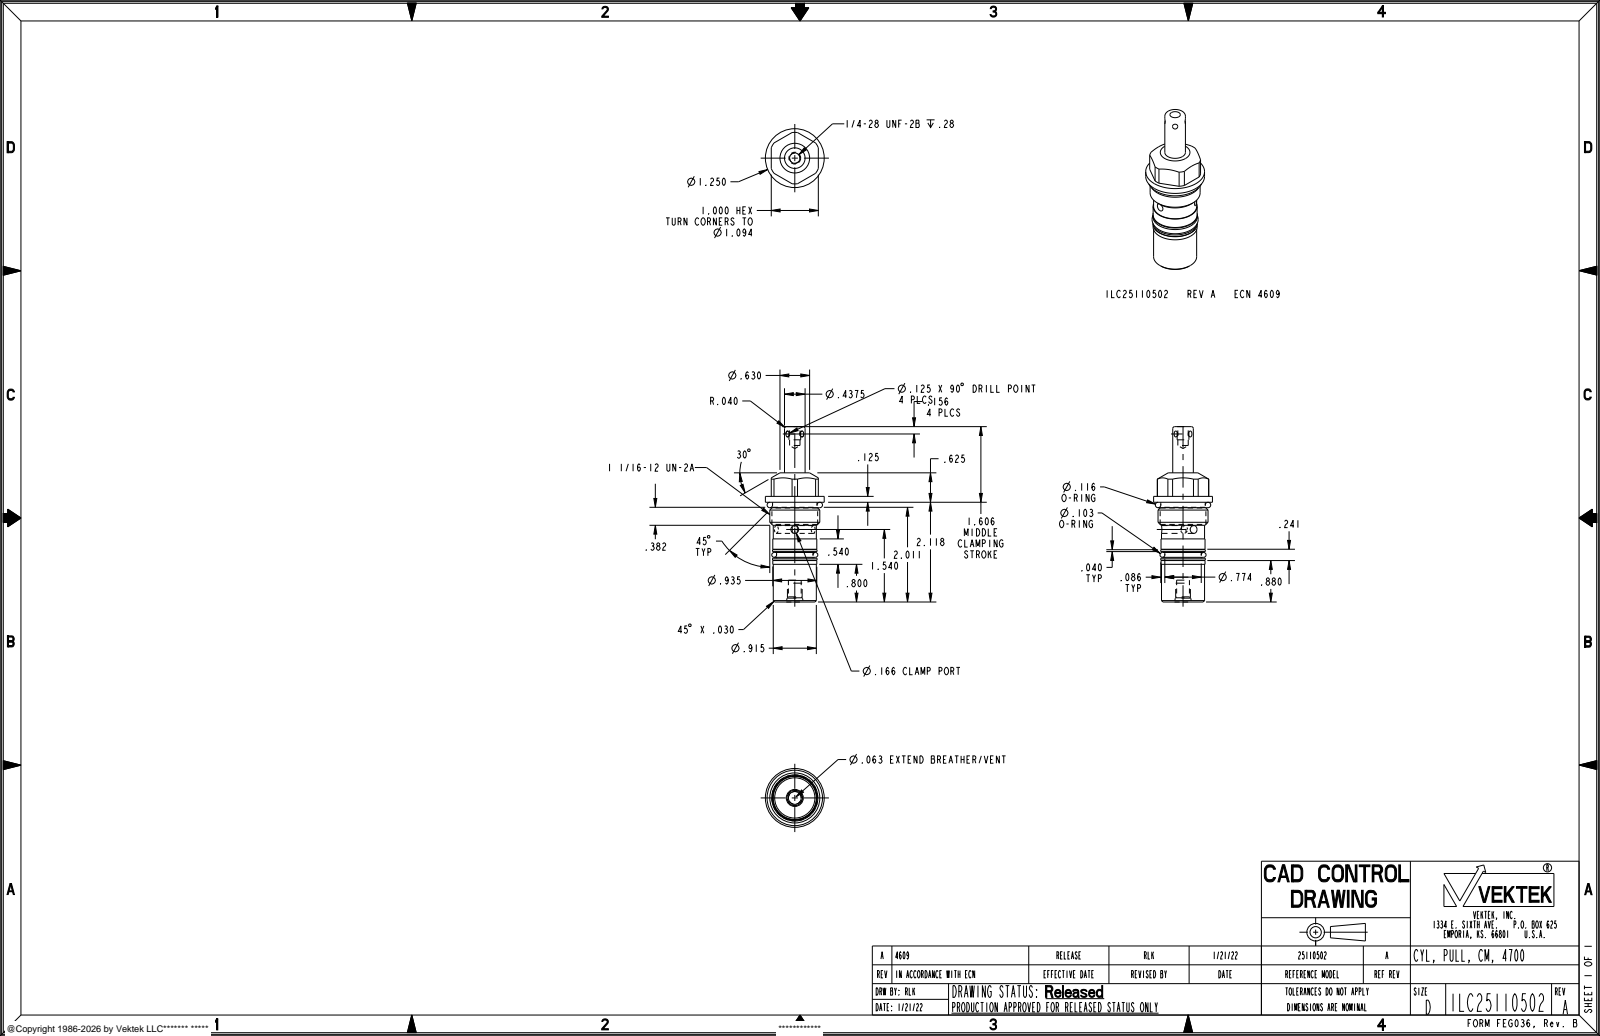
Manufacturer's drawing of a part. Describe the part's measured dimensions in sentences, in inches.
The part is named "ILC25110502". Its 3-D file was written by "CREO PARAMETRIC BY PTC INC, 2021164 (AUTOMOTIVE_DESIGN)". It is 3 solids with 106 faces: 26 planar, 48 cylindrical and 32 other. Overall it measures 3.724 by 1.25 by 1.25 inches. Its volume is 2.13 cubic inches and its surface area 18.4 square inches. Round holes: 3 of diameter 0.166, 1 of diameter 0.221, 1 of diameter 0.272. Round bosses or shafts: 1 of diameter 1.25, 1 of diameter 1.063, 1 of diameter 0.972, 1 of diameter 0.946, 1 of diameter 0.945, 1 of diameter 0.935, 1 of diameter 0.915, 1 of diameter 0.774. Partial cylindrical surfaces (rounded edges, fillets, slot ends): 1 of radius 0.547. The main face-to-face distances are 1, 2.118, 0.05, 0.191, 2.243, 0.125, 0.89, 0.93, 1.07, 1.111.
